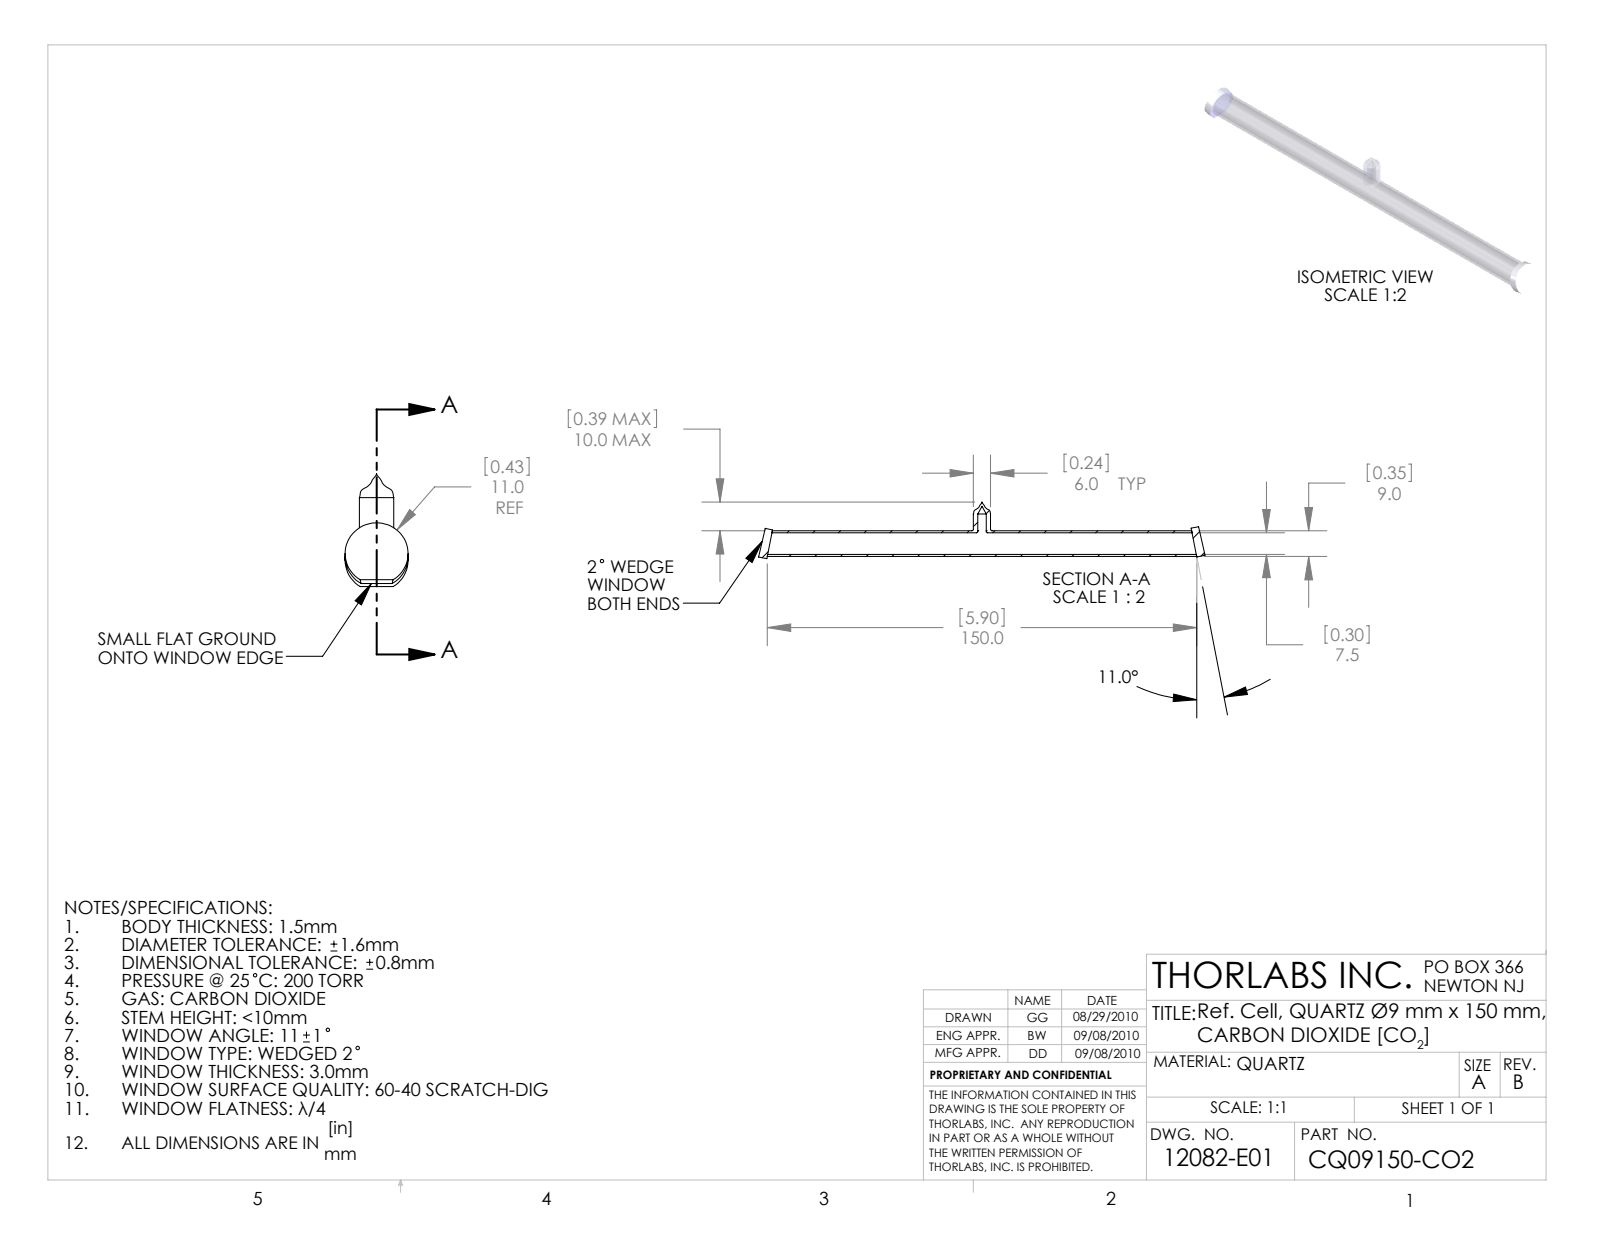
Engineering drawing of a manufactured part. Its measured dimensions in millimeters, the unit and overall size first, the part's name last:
Units: millimetres
Overall size (bounding box): 155.95 × 19.74 × 11
Round holes (diameter × count): ⌀2.91 ×1, ⌀3 ×1, ⌀7.5 ×1
Round bosses / shafts (diameter × count): ⌀11 ×2, ⌀9 ×1, ⌀6 ×1
Volume: 3 563 mm³ · Surface area: 8 494 mm²
Bodies: 3 solids, 33 faces (8 planar, 17 cylindrical, 8 other)
Part name (STEP PRODUCT): 12082-E0W
STEP written by: SolidWorks 2009 (AUTOMOTIVE_DESIGN)
